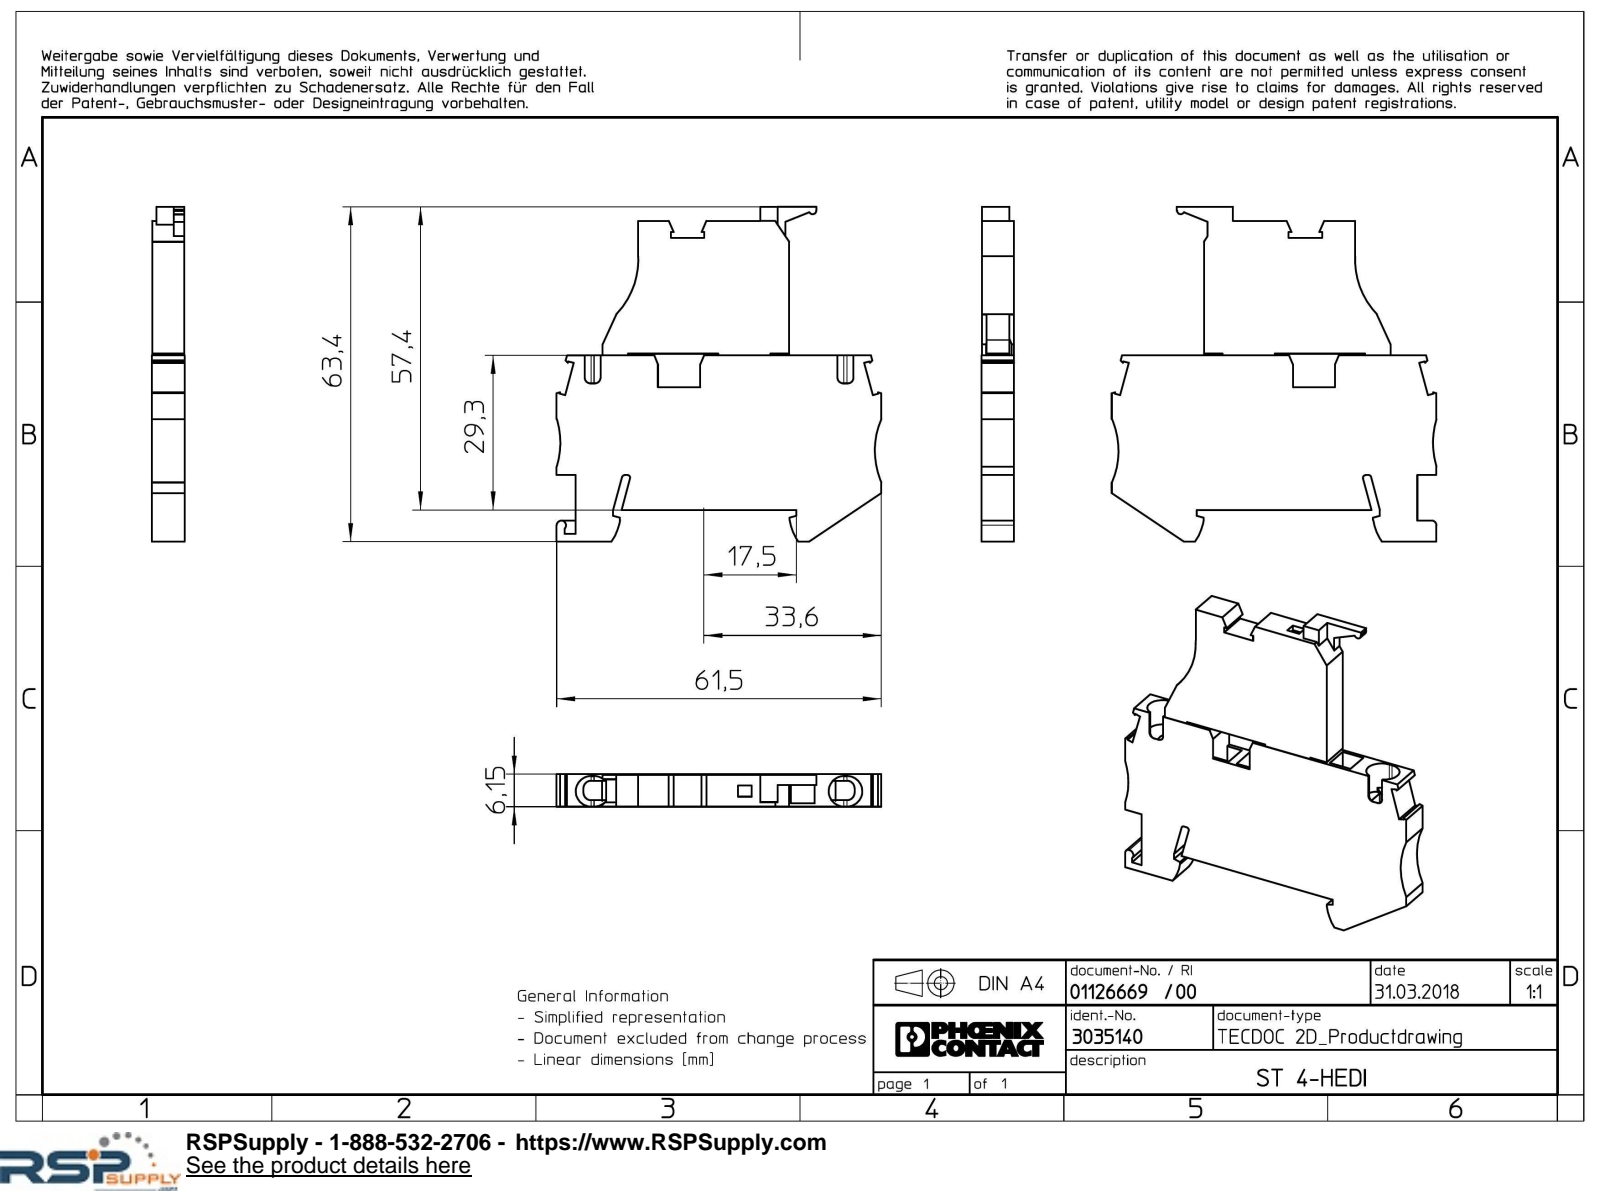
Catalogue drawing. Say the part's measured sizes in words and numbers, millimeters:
The part is named "ST4-HEDI-Select". Its 3-D file was written by "Creo Elements/Direct Modeling 20.1A 29-Sep-2018 (C) Parametric Technology GmbH (AUTOMOTIVE_DESIGN)". It is 1 solid with 166 faces: 136 planar, 24 cylindrical and 6 other. Overall it measures 63.38 by 61.5 by 6.15 millimeters. Its volume is 14 316 cubic millimeters and its surface area 8 178 square millimeters. Partial cylindrical surfaces (rounded edges, fillets, slot ends): 4 of radius 1, 4 of radius 1.45, 4 of radius 2.9, 3 of radius 15, 2 of radius 0.5, 2 of radius 9.5, 1 of radius 0.1, 1 of radius 0.7. The main face-to-face distances are 6.15, 6.07, 6.12, 6.04, 4.85, 0.35, 29.25, 29.6, 0.57, 3.15.
